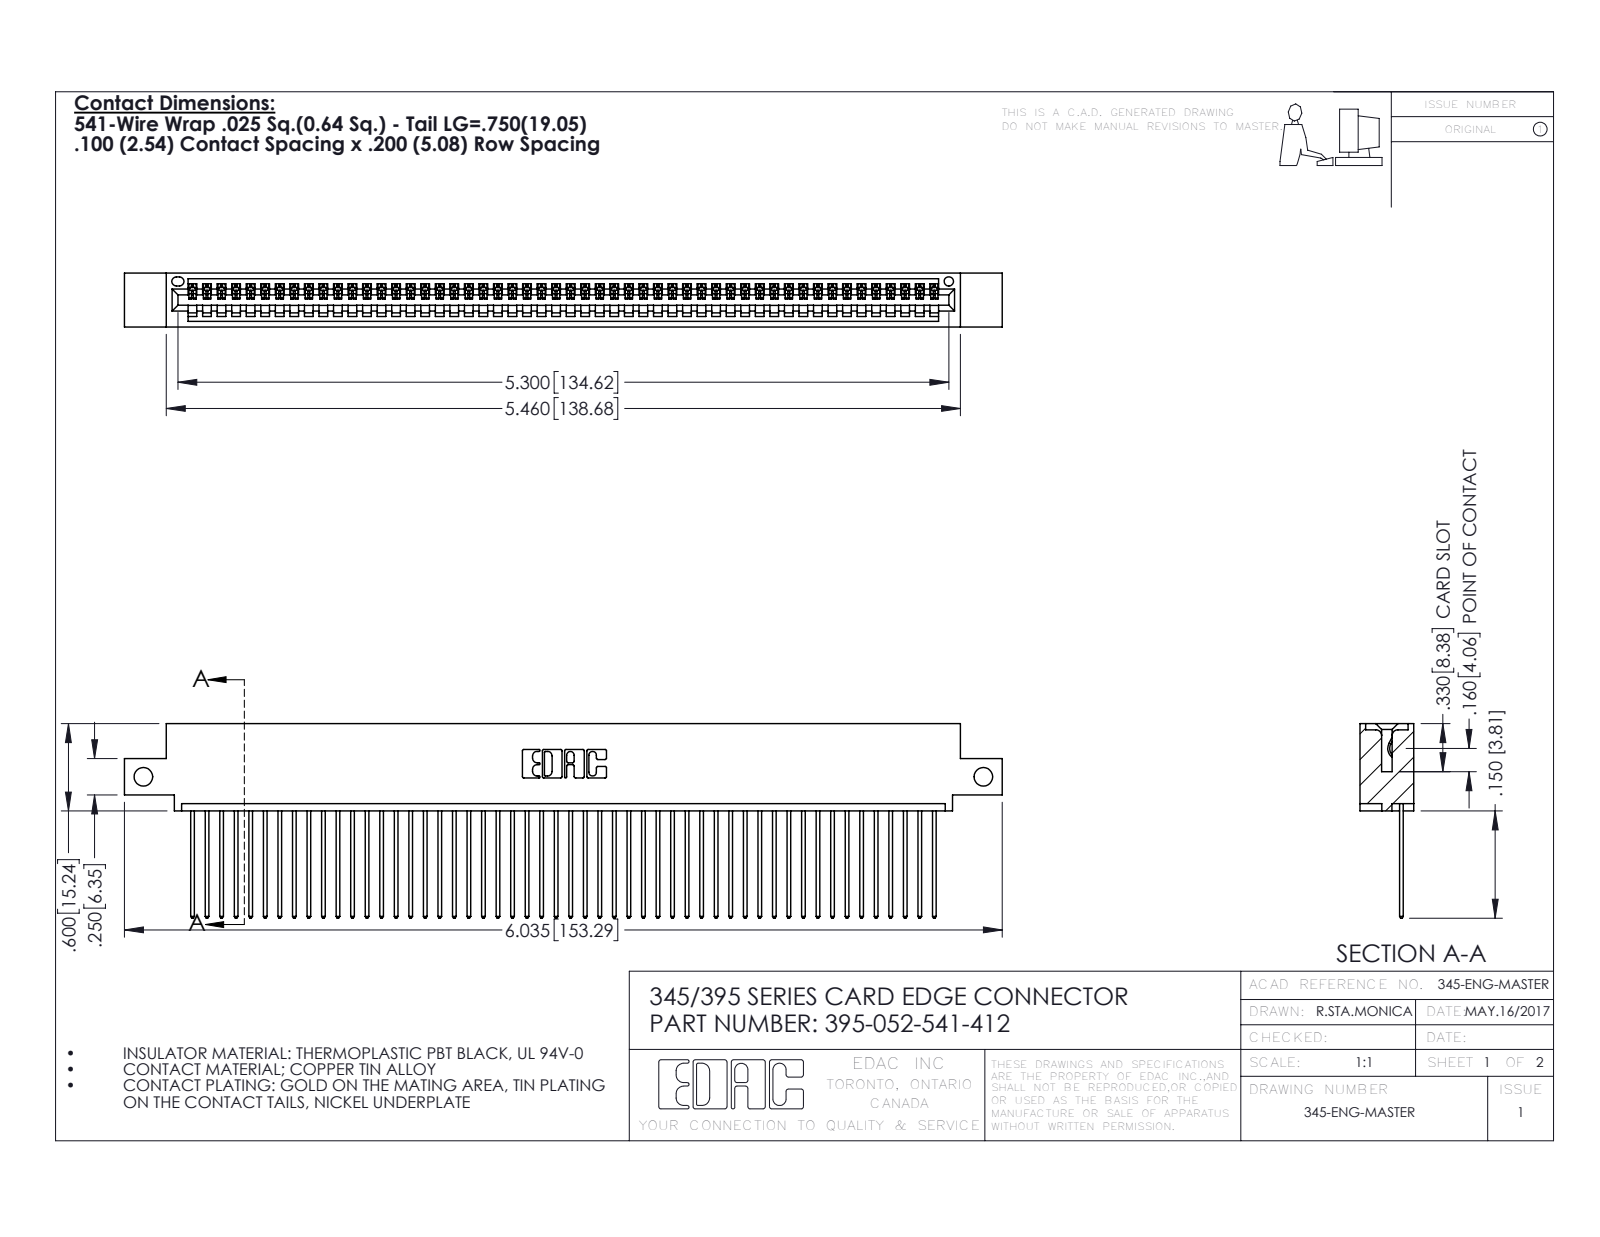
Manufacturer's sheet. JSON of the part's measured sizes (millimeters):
{"part_name": "345-292-001_345-293-141; 345 Part_0.110 Offset - Side Mount; 395-052-541-412", "step_written_by": "SolidWorks 2016 (CONFIG_CONTROL_DESIGN)", "units": "millimeters", "bodies": {"solids": 53, "faces": 3146, "planar": 2164, "cylindrical": 982, "other": 0}, "overall_size": [153.3, 34, 9.4], "volume_mm3": 14700, "surface_area_mm2": 20550, "round_holes": [[3.3, 2], [1.6, 1]], "partial_cylinders_radius": [[0.2, 104], [0.3, 104], [0.3, 22], [0.2, 6], [0.8, 6], [0.7, 3], [0.8, 2], [1, 2]], "face_to_face_distances": [1.8, 7.6, 2.5, 6.9, 0.6, 9.4, 5.1, 5.7, 3.8, 1.8], "hole_center_spacings": [146.7]}
